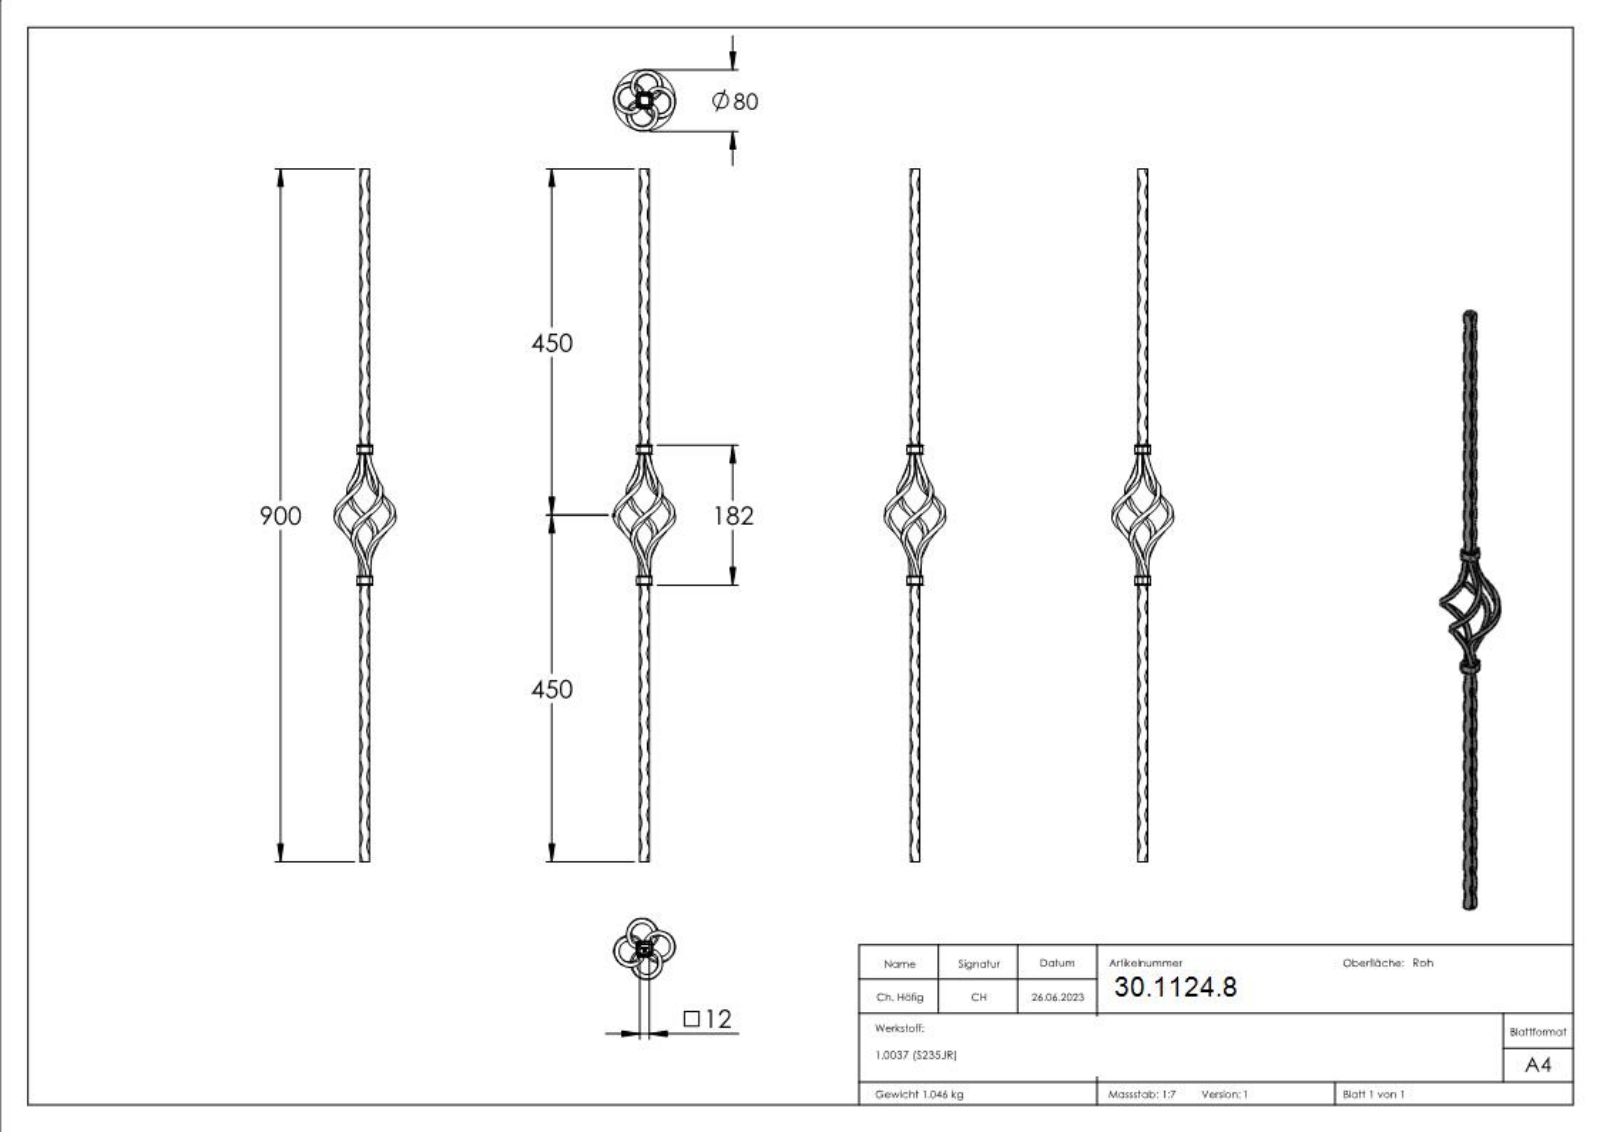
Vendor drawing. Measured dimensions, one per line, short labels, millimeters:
name: 1253
written by: SolidWorks 2018 (CONFIG_CONTROL_DESIGN)
unit: mm
bodies: 11 solids, 611 faces (238 planar, 99 cylindrical, 274 other)
size: 900 × 83.54 × 80.07
volume: 218 228 mm³; area: 81 015 mm²
bosses: 1× ⌀12
rounds: 32× R0.4, 16× R0.1, 8× R12.72, 4× R1, 4× R3.6, 4× R4
face distances: 12, 1, 6, 13, 170, 14, 176, 0.5, 164, 5.5
